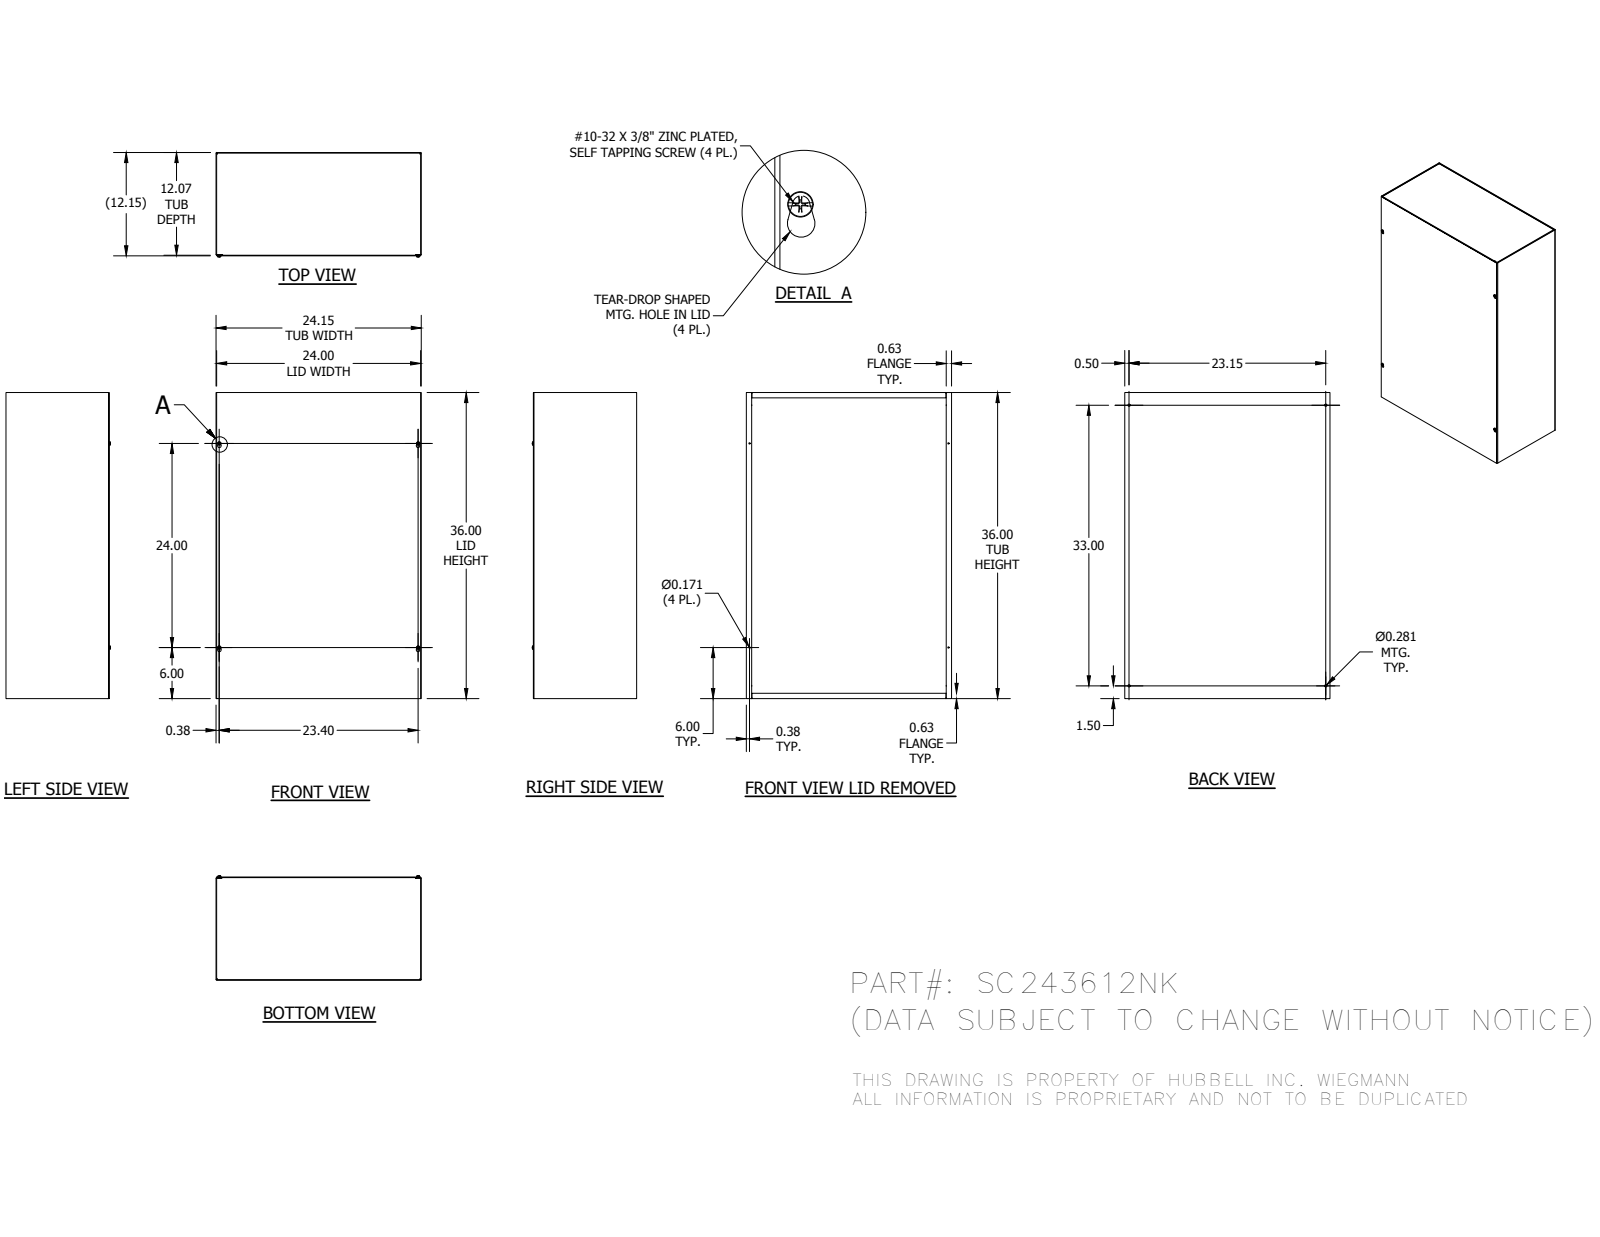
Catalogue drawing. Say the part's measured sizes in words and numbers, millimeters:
The part is named "SC243612NKBLR; SC2412NKTB; SC2436LPA; 37214 (+1 more)". Its 3-D file was written by "Autodesk Inventor 2014 (AUTOMOTIVE_DESIGN)". It is 8 solids with 320 faces: 192 planar, 44 cylindrical and 84 other. Overall it measures 914.4 by 613.36 by 311.91 millimeters. Its volume is 3 982 000 cubic millimeters and its surface area 4 259 000 square millimeters. Round holes: 4 of diameter 4.34, 4 of diameter 7.14. Round bosses or shafts: 4 of diameter 4.83. Partial cylindrical surfaces (rounded edges, fillets, slot ends): 12 of radius 0.4, 12 of radius 2.28, 4 of radius 3.17, 4 of radius 5.16. The main face-to-face distances are 1.88, 306.68, 304.8, 308.56, 611.48, 912.52, 609.6, 613.36, 914.4, 910.64. The hole center spacings are 114.34, 602.08, 723.91, 934.59, 587.96, 594.3, 609.6, 838.2.
